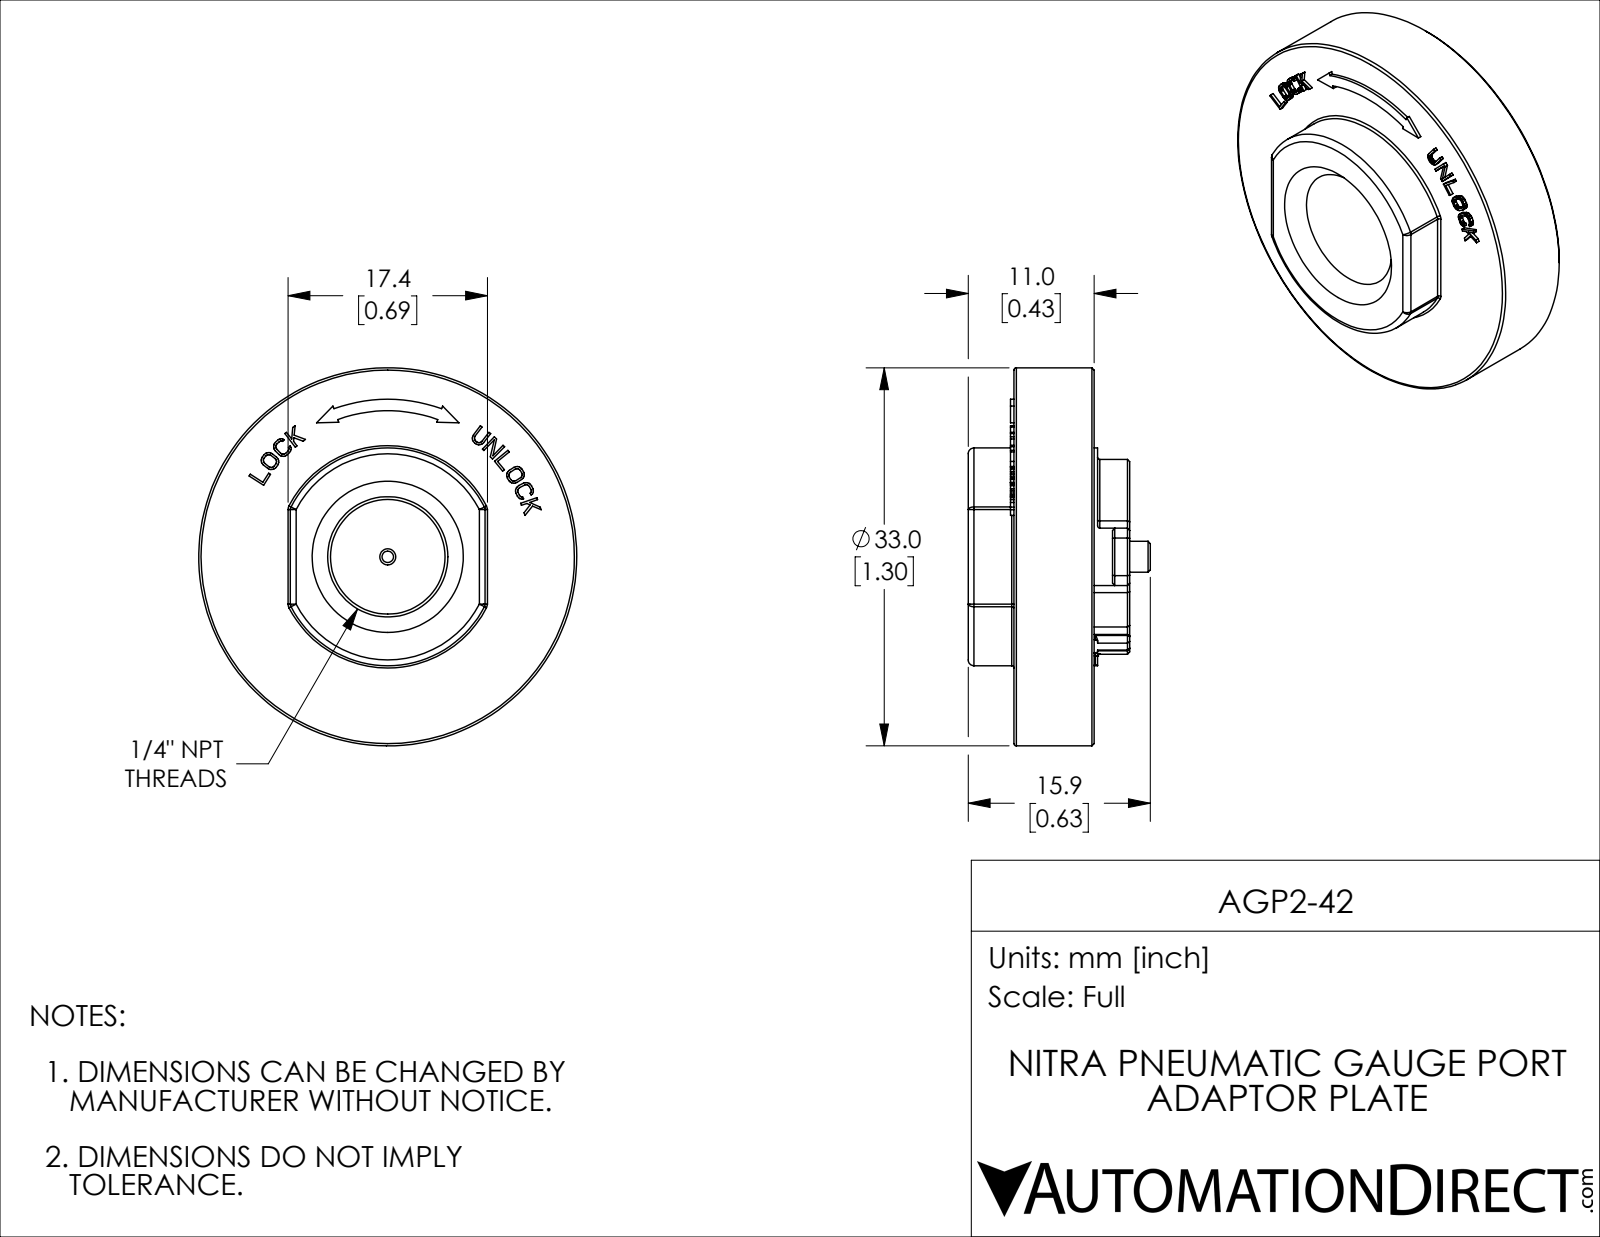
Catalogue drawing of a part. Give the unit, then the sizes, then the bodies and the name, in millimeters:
Units: millimetres
Overall size (bounding box): 33 × 33 × 15.9
Round holes (diameter × count): ⌀1 ×1
Round bosses / shafts (diameter × count): ⌀33 ×1, ⌀19 ×1, ⌀2.7 ×1
Partial cylindrical surfaces — rounded edges, fillets, slot ends (radius × count): R0.2 ×30, R0.5 ×14, R1 ×8, R8.5 ×1, R11.5 ×1, R12.8 ×1, R13.7 ×1, R15 ×1
Main face-to-face distances: 7, 10.1, 3.1, 2, 5, 8.1, 6, 4, 11, 14.1
Volume: 5 750 mm³ · Surface area: 3 917 mm²
Bodies: 1 solid, 501 faces (307 planar, 93 cylindrical, 101 other)
Part name (STEP PRODUCT): AGP2-42
STEP written by: SolidWorks 2019 (CONFIG_CONTROL_DESIGN)
